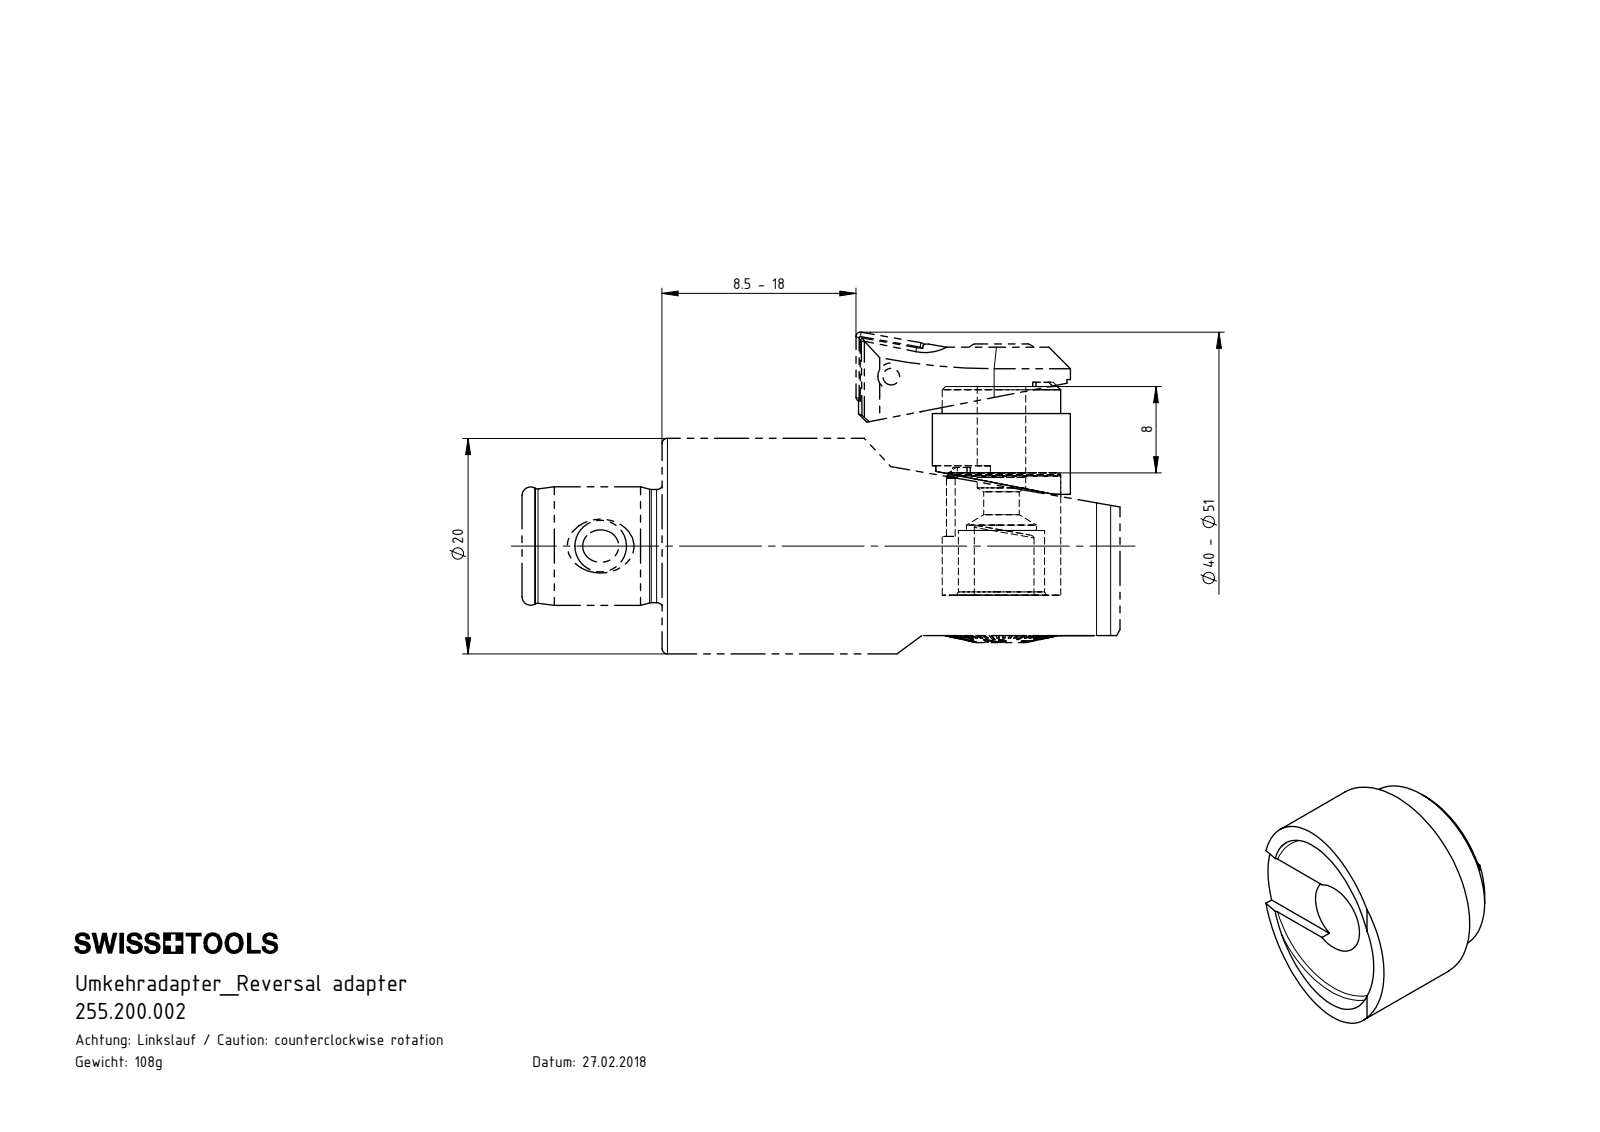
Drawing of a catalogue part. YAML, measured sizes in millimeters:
part_name: "F20-U00.001.008_B; 255.200.002"
step_written_by: "SolidWorks 2017 (CONFIG_CONTROL_DESIGN)"
units: millimeters
bodies: {solids: 1, faces: 29, planar: 13, cylindrical: 11, other: 5}
overall_size: [12.8, 12.8, 10.4]
volume: 843
surface_area: 719
round_holes:
  - {diameter: 4.5, count: 1}
  - {diameter: 11, count: 1}
round_bosses_or_shafts:
  - {diameter: 12.8, count: 1}
partial_cylinders:
  - {radius: 0.3, count: 2}
face_to_face_distances: [8, 2.5, 5.5, 7.35, 4.85, 0.65, 0.4, 2.9, 7.75, 8.4]
